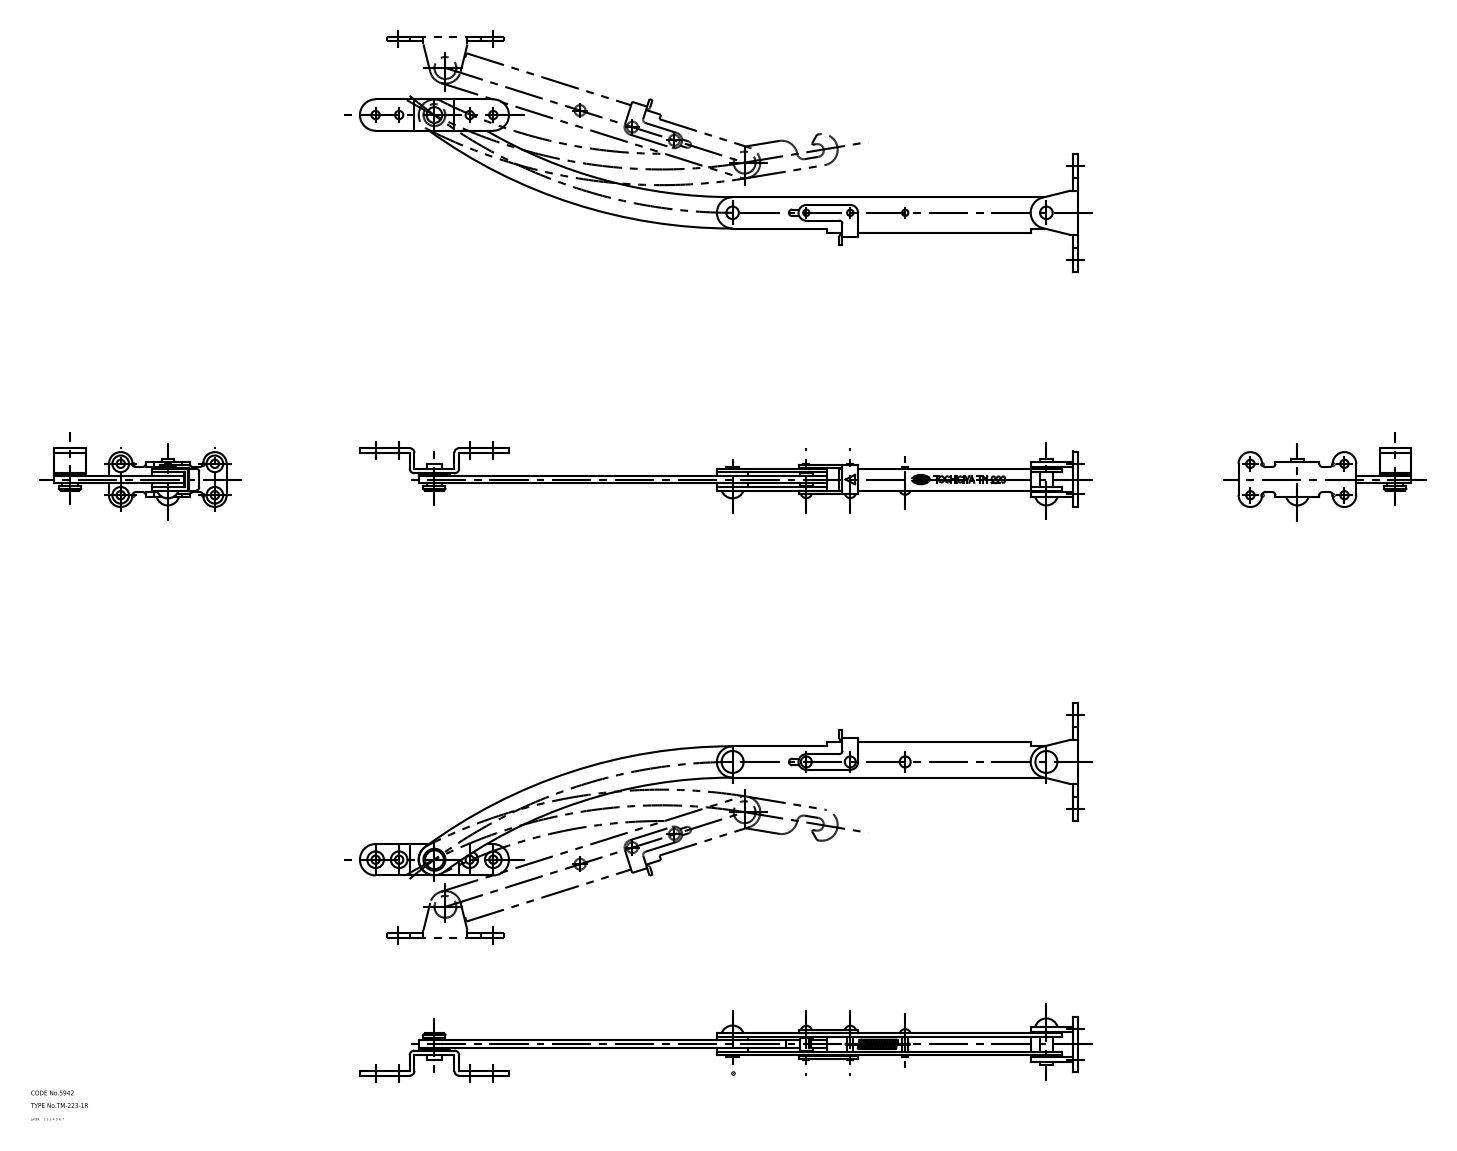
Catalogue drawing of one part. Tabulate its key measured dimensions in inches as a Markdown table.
| quantity | value |
| --- | --- |
| part name | spacer_A_mr-1; spacer_C_mr-1; pin_A_mr-1; stopper_mr (+8 more) |
| STEP written by | CADfix (AUTOMOTIVE_DESIGN) |
| units | inches |
| bodies | 18 solids, 301 faces (0 planar, 0 cylindrical, 301 other) |
| overall size | 18.013 × 4.324 × 1.476 |
| volume | 4.252 in³ |
| surface area | 91.23 in² |
